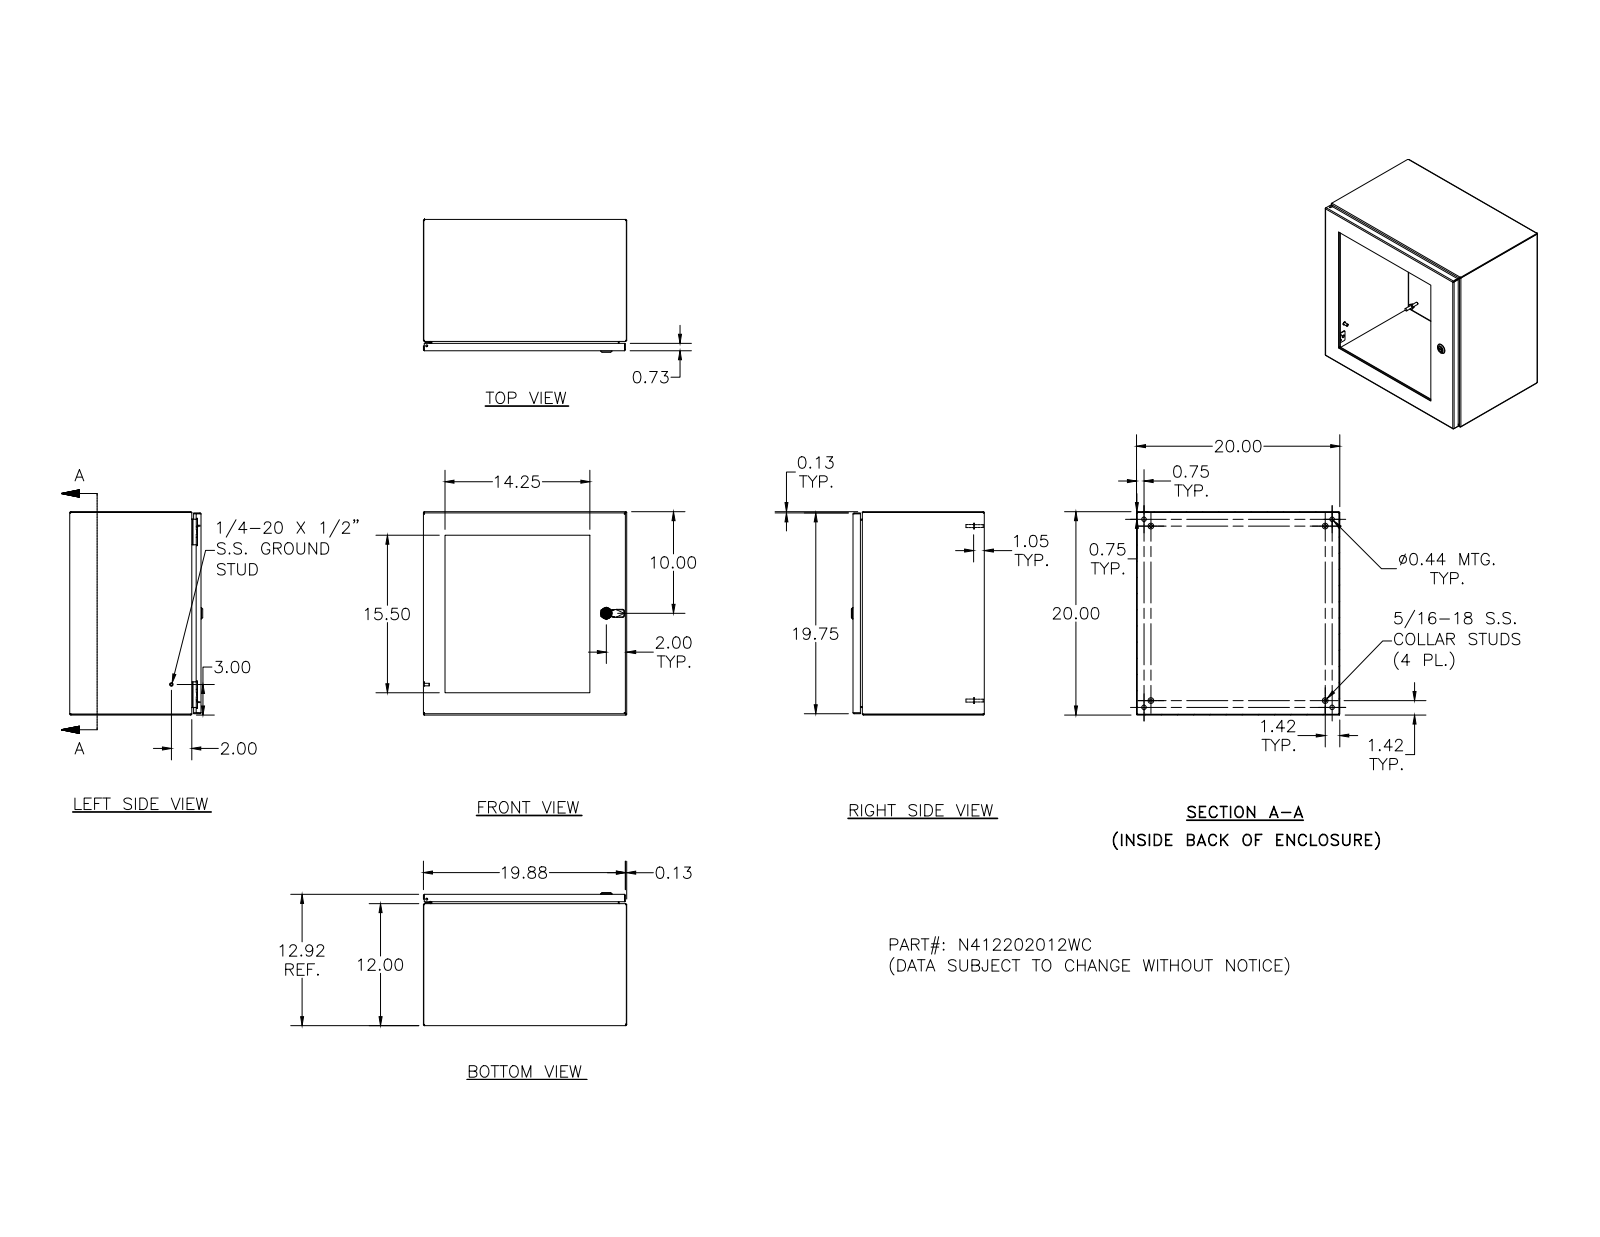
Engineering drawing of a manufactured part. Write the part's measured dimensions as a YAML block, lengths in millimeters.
part_name: "N412202012WC"
step_written_by: "SolidWorks 2018 (AUTOMOTIVE_DESIGN)"
units: millimeters
bodies: {solids: 69, faces: 2019, planar: 753, cylindrical: 617, other: 649}
overall_size: [508, 508, 332.1]
volume: 3181000
surface_area: 2648000
round_holes:
  - {diameter: 4, count: 18}
  - {diameter: 7.1, count: 16}
  - {diameter: 4.8, count: 5}
  - {diameter: 2.4, count: 4}
  - {diameter: 3.9, count: 4}
  - {diameter: 4.2, count: 4}
  - {diameter: 4.4, count: 4}
  - {diameter: 11.1, count: 4}
  - {diameter: 4.7, count: 1}
  - {diameter: 5, count: 1}
  - {diameter: 8, count: 1}
  - {diameter: 10, count: 1}
round_bosses_or_shafts:
  - {diameter: 8.6, count: 16}
  - {diameter: 4.8, count: 16}
  - {diameter: 6.4, count: 10}
  - {diameter: 14.3, count: 4}
  - {diameter: 9.1, count: 4}
  - {diameter: 8.1, count: 4}
  - {diameter: 7.6, count: 4}
  - {diameter: 7, count: 4}
partial_cylinders:
  - {radius: 0.8, count: 34}
  - {radius: 0.3, count: 30}
  - {radius: 1.3, count: 26}
  - {radius: 2.7, count: 24}
  - {radius: 0.4, count: 18}
  - {radius: 3.2, count: 16}
  - {radius: 0.5, count: 13}
  - {radius: 0.8, count: 8}
face_to_face_distances: [1.9, 506.1, 326.2, 508, 504.2, 324.3, 6.4, 319.9, 318, 328.1]
hole_center_spacings: [101.6, 203.2, 406.6, 406.4, 437.4, 158, 218.1, 254.9]
